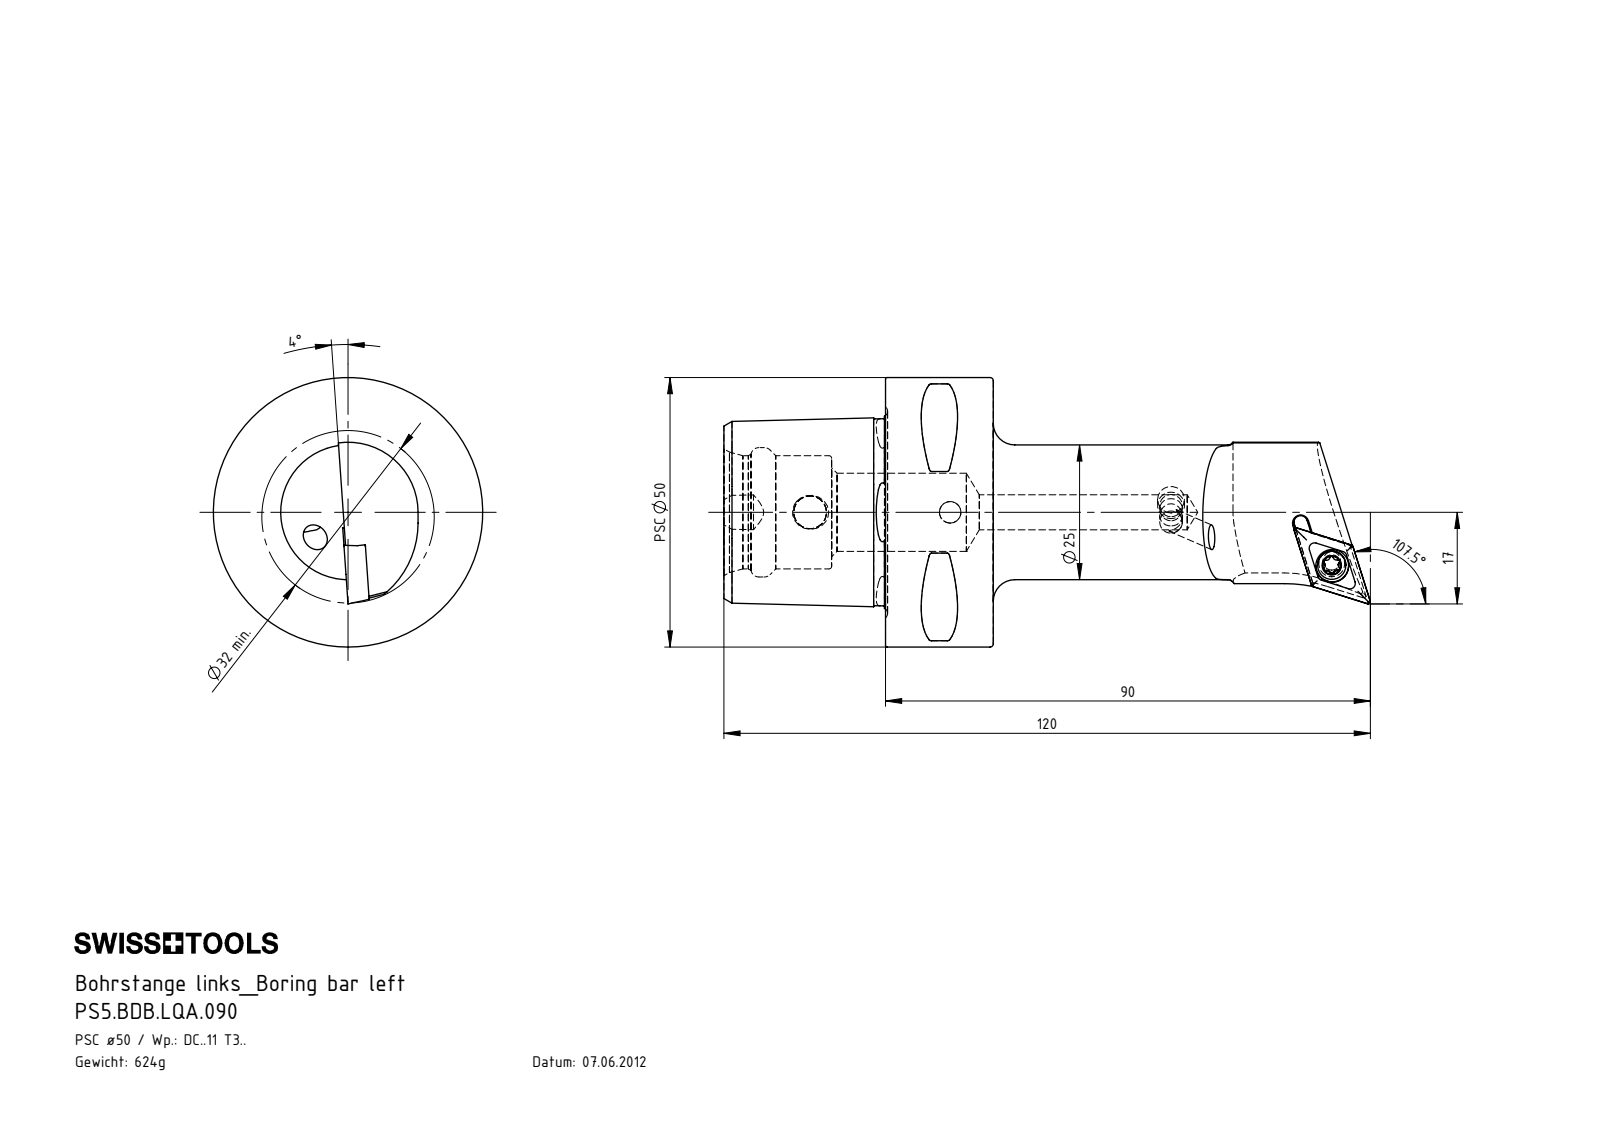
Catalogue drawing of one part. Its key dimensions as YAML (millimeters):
part_name: "DCMT11T304; WCB-ER2.001.009_A; KVT_MB_600_050; PS5-BDB.LQA.090_A (+1 more)"
step_written_by: "SolidWorks 2017 (AUTOMOTIVE_DESIGN)"
units: millimeters
bodies: {solids: 5, faces: 287, planar: 53, cylindrical: 75, other: 159}
overall_size: [120, 50, 50]
volume: 79296
surface_area: 19662
round_holes:
  - {diameter: 4, count: 2}
  - {diameter: 4.2, count: 2}
  - {diameter: 6.1, count: 2}
  - {diameter: 3.3, count: 1}
  - {diameter: 4.4, count: 1}
  - {diameter: 5, count: 1}
  - {diameter: 6.5, count: 1}
  - {diameter: 14.5, count: 1}
  - {diameter: 21, count: 1}
  - {diameter: 24, count: 1}
round_bosses_or_shafts:
  - {diameter: 50, count: 1}
  - {diameter: 25, count: 1}
  - {diameter: 5.25, count: 1}
  - {diameter: 5, count: 1}
  - {diameter: 4, count: 1}
partial_cylinders:
  - {radius: 0.5, count: 8}
  - {radius: 0.34, count: 6}
  - {radius: 0.59, count: 6}
  - {radius: 1.25, count: 1}
  - {radius: 3, count: 1}
  - {radius: 4, count: 1}
  - {radius: 13, count: 1}
  - {radius: 17, count: 1}
face_to_face_distances: [20, 30, 50, 19.18, 3.67, 44.4, 10, 29.8, 9.8, 20.2]
hole_center_spacings: [26]
